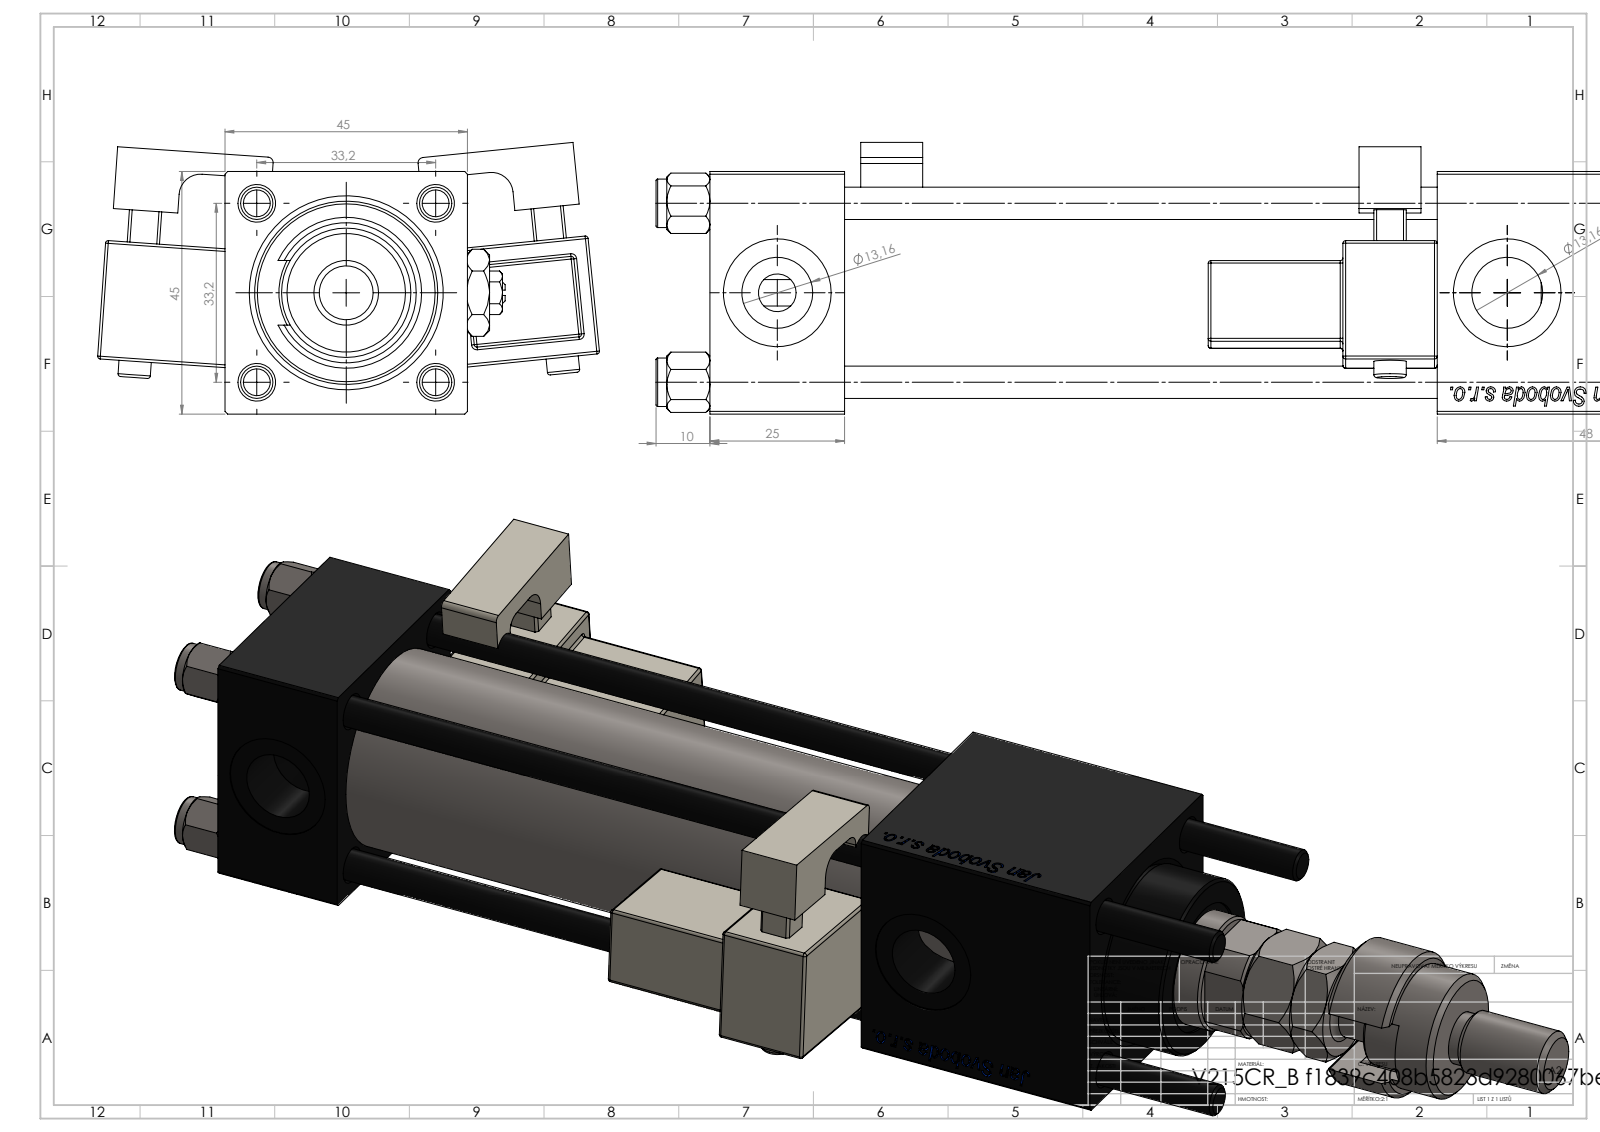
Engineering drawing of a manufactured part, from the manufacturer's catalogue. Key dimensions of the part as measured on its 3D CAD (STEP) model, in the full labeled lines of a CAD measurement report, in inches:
Part name (STEP PRODUCT): MFA; NUT_M5_B; V215CR_VCP_B; V215CR_B_TYCINKA (+5 more)
STEP written by: SolidWorks 2019 (CONFIG_CONTROL_DESIGN)
Units: inches
Bodies: 17 solids, 1499 faces (568 planar, 161 cylindrical, 770 other)
Overall size (bounding box): 10.984 × 3.667 × 1.984
Volume: 19.57 in³ · Surface area: 185.4 in²
Round holes (diameter × count): ⌀0.236 ×4, ⌀0.276 ×2, ⌀0.518 ×2, ⌀0.787 ×2, ⌀0.413 ×1, ⌀0.866 ×1, ⌀0.945 ×1, ⌀0.984 ×1, ⌀1.26 ×1, ⌀1.299 ×1
Round bosses / shafts (diameter × count): ⌀0.354 ×4, ⌀0.236 ×2, ⌀1.496 ×1, ⌀1.339 ×1, ⌀1.102 ×1, ⌀0.709 ×1, ⌀0.472 ×1, ⌀0.433 ×1
Partial cylindrical surfaces — rounded edges, fillets, slot ends (radius × count): R0.02 ×48, R0.039 ×2, R0.098 ×2, R0.157 ×2, R0.384 ×1, R0.413 ×1
Main face-to-face distances: 1.772, 0.984, 5.315, 4.331, 0.118, 7.205, 0.571, 0.591, 3.642, 0.689
Hole centre spacings: 0.924, 1.307, 1.848, 5.335
